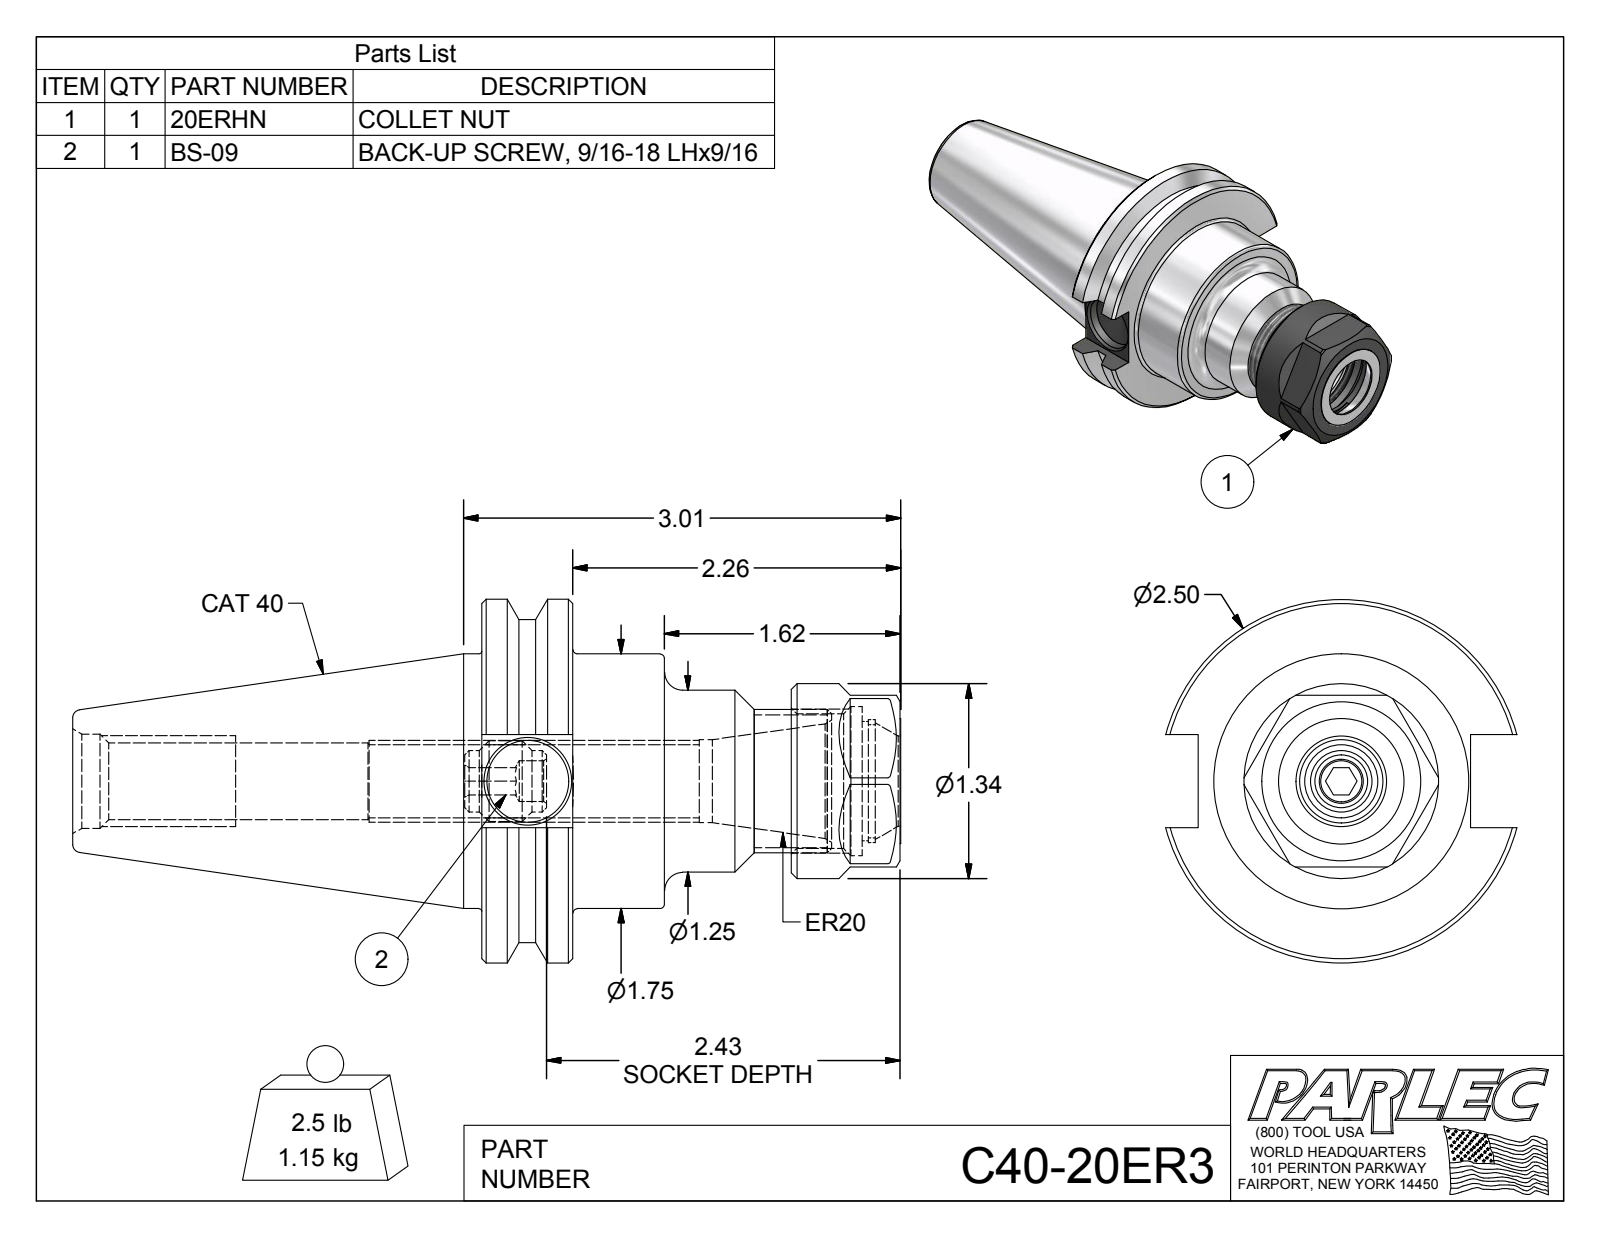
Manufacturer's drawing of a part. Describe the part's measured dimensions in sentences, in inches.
The part is named "C40-20ER3; C40-20ER3-1; 20ERHN; BS-09". Its 3-D file was written by "Autodesk Inventor 2012 (AUTOMOTIVE_DESIGN)". It is 3 solids with 110 faces: 44 planar, 26 cylindrical and 40 other. Overall it measures 5.693 by 2.5 by 2.417 inches. Its volume is 8.912 cubic inches and its surface area 49.44 square inches. Round holes: 1 of diameter 0.281, 1 of diameter 0.502, 1 of diameter 0.527, 1 of diameter 0.563, 1 of diameter 0.57, 1 of diameter 0.62, 1 of diameter 0.648, 1 of diameter 0.82, 1 of diameter 0.925, 1 of diameter 1.024. Round bosses or shafts: 1 of diameter 2.5, 1 of diameter 2.219, 1 of diameter 1.75, 1 of diameter 1.339, 1 of diameter 1.25, 1 of diameter 0.984, 1 of diameter 0.86, 1 of diameter 0.555. Partial cylindrical surfaces (rounded edges, fillets, slot ends): 1 of radius 0.423. The main face-to-face distances are 0.625, 1.181, 1.255, 0.63, 2.127, 1.502, 0.872, 0.27, 0.911, 2.875. The hole center spacings are 0.037.
